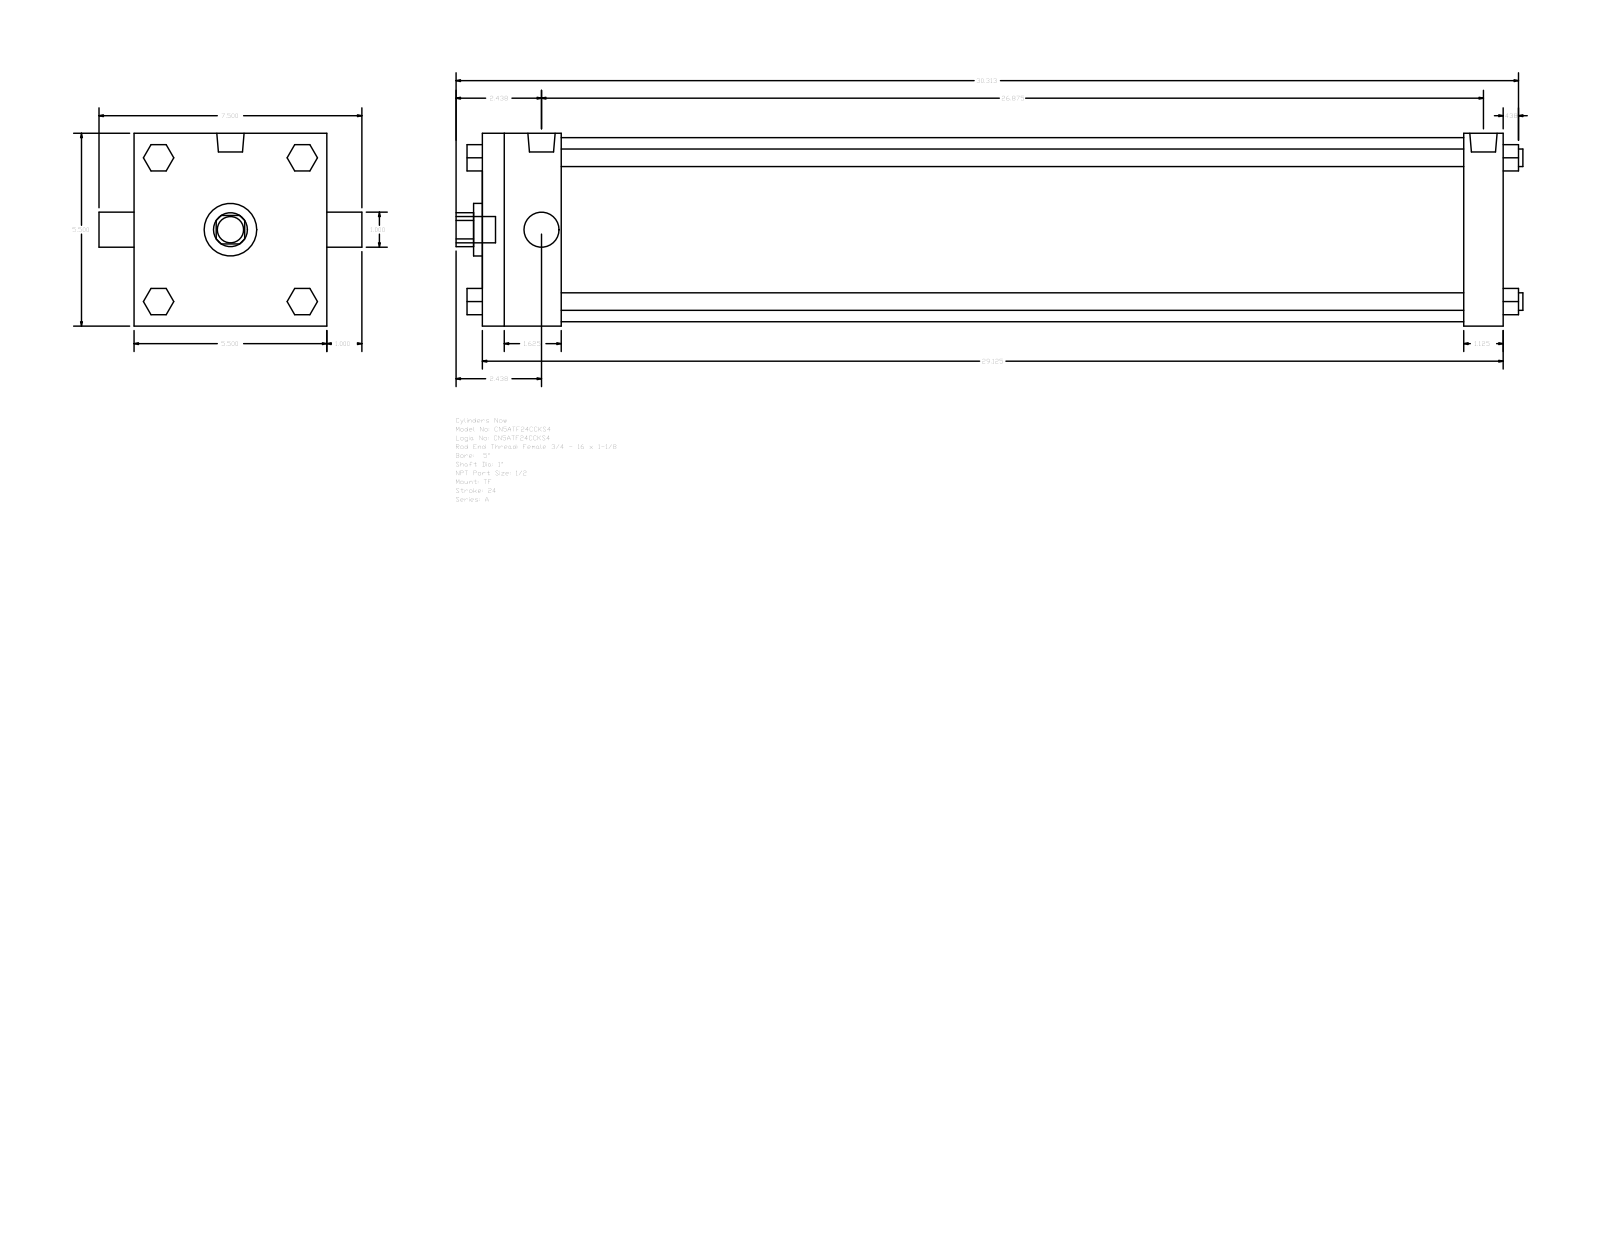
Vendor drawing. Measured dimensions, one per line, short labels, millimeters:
name: A_TF__0500_1
written by: GSSL Pune (CONFIG_CONTROL_DESIGN)
unit: mm
bodies: 0 solids, 120 faces (92 planar, 28 cylindrical, 0 other)
size: 773.11 × 190.5 × 139.7
holes: 2× ⌀25.4, 1× ⌀38.1, 1× ⌀133.35
bosses: 4× ⌀12.7, 3× ⌀8.73, 2× ⌀19.77, 1× ⌀19.05
rounds: 1× R12.29
face distances: 139.7, 739.78, 711.2, 28.58, 57.15, 654.05, 682.63, 19.05, 52.07, 90.18
